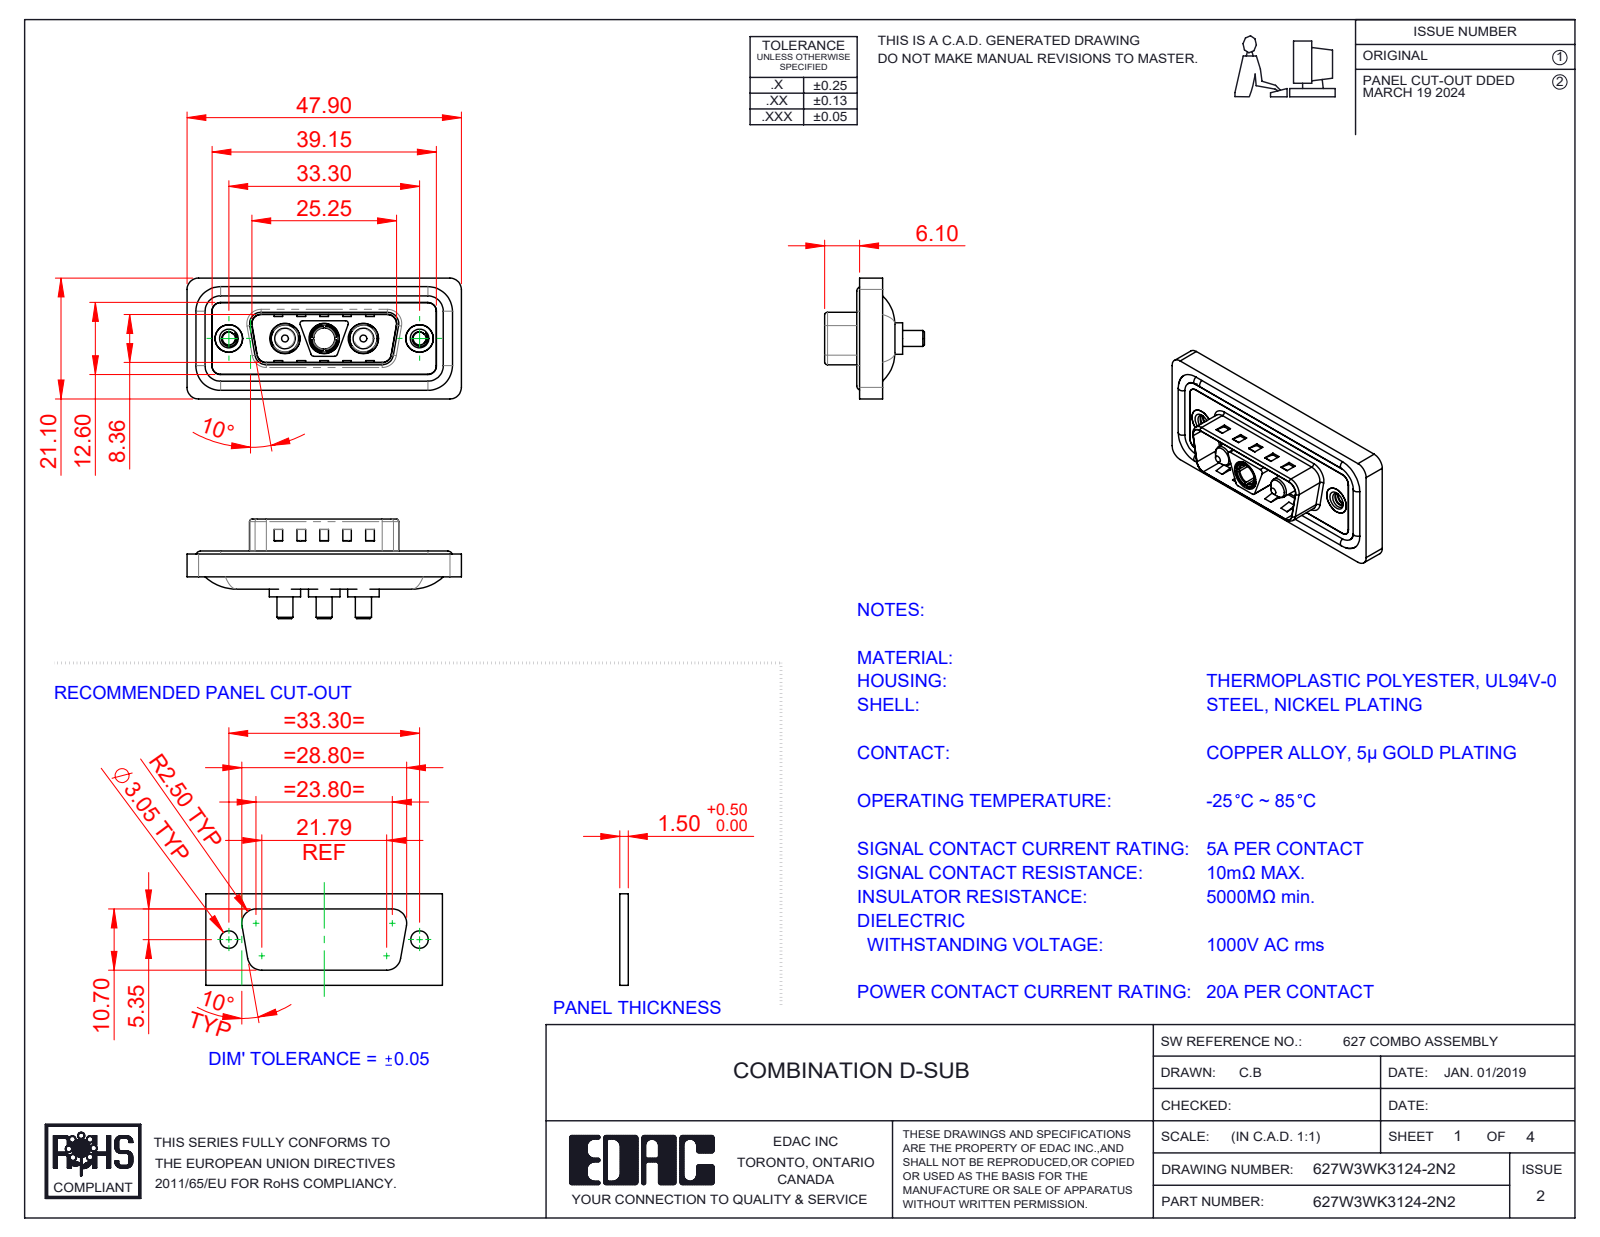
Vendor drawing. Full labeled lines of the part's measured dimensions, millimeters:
Part name (STEP PRODUCT): Power Socket_20A S; 627Combo Housing_3WK3; Power Pin_20A S; 627Combo Shell Rear_15 Contacts (+4 more)
STEP written by: SolidWorks 2023 (CONFIG_CONTROL_DESIGN)
Units: millimetres
Bodies: 13 solids, 609 faces (231 planar, 250 cylindrical, 128 other)
Overall size (bounding box): 47.9 × 21.1 × 17.4
Volume: 5 688 mm³ · Surface area: 9 127 mm²
Round holes (diameter × count): ⌀4.85 ×3, ⌀5.3 ×3, ⌀2.26 ×2, ⌀4 ×2, ⌀4.8 ×2, ⌀5 ×2, ⌀3.7 ×1
Round bosses / shafts (diameter × count): ⌀1.6 ×4, ⌀5.5 ×3, ⌀5.2 ×3, ⌀4.75 ×3, ⌀3.75 ×3, ⌀2.8 ×3, ⌀4.9 ×2, ⌀3.6 ×2
Partial cylindrical surfaces — rounded edges, fillets, slot ends (radius × count): R1.5 ×26, R2 ×20, R0.5 ×12, R1.6 ×8, R0.25 ×4, R0.6 ×4, R0.65 ×4, R0.9 ×4
Main face-to-face distances: 0.4, 1.1, 1.5, 0.5, 1.6, 3.1, 2.9, 4, 0.82, 9.58
Hole centre spacings: 6.85, 9.8, 16.65, 23.5, 13.7, 33.3
